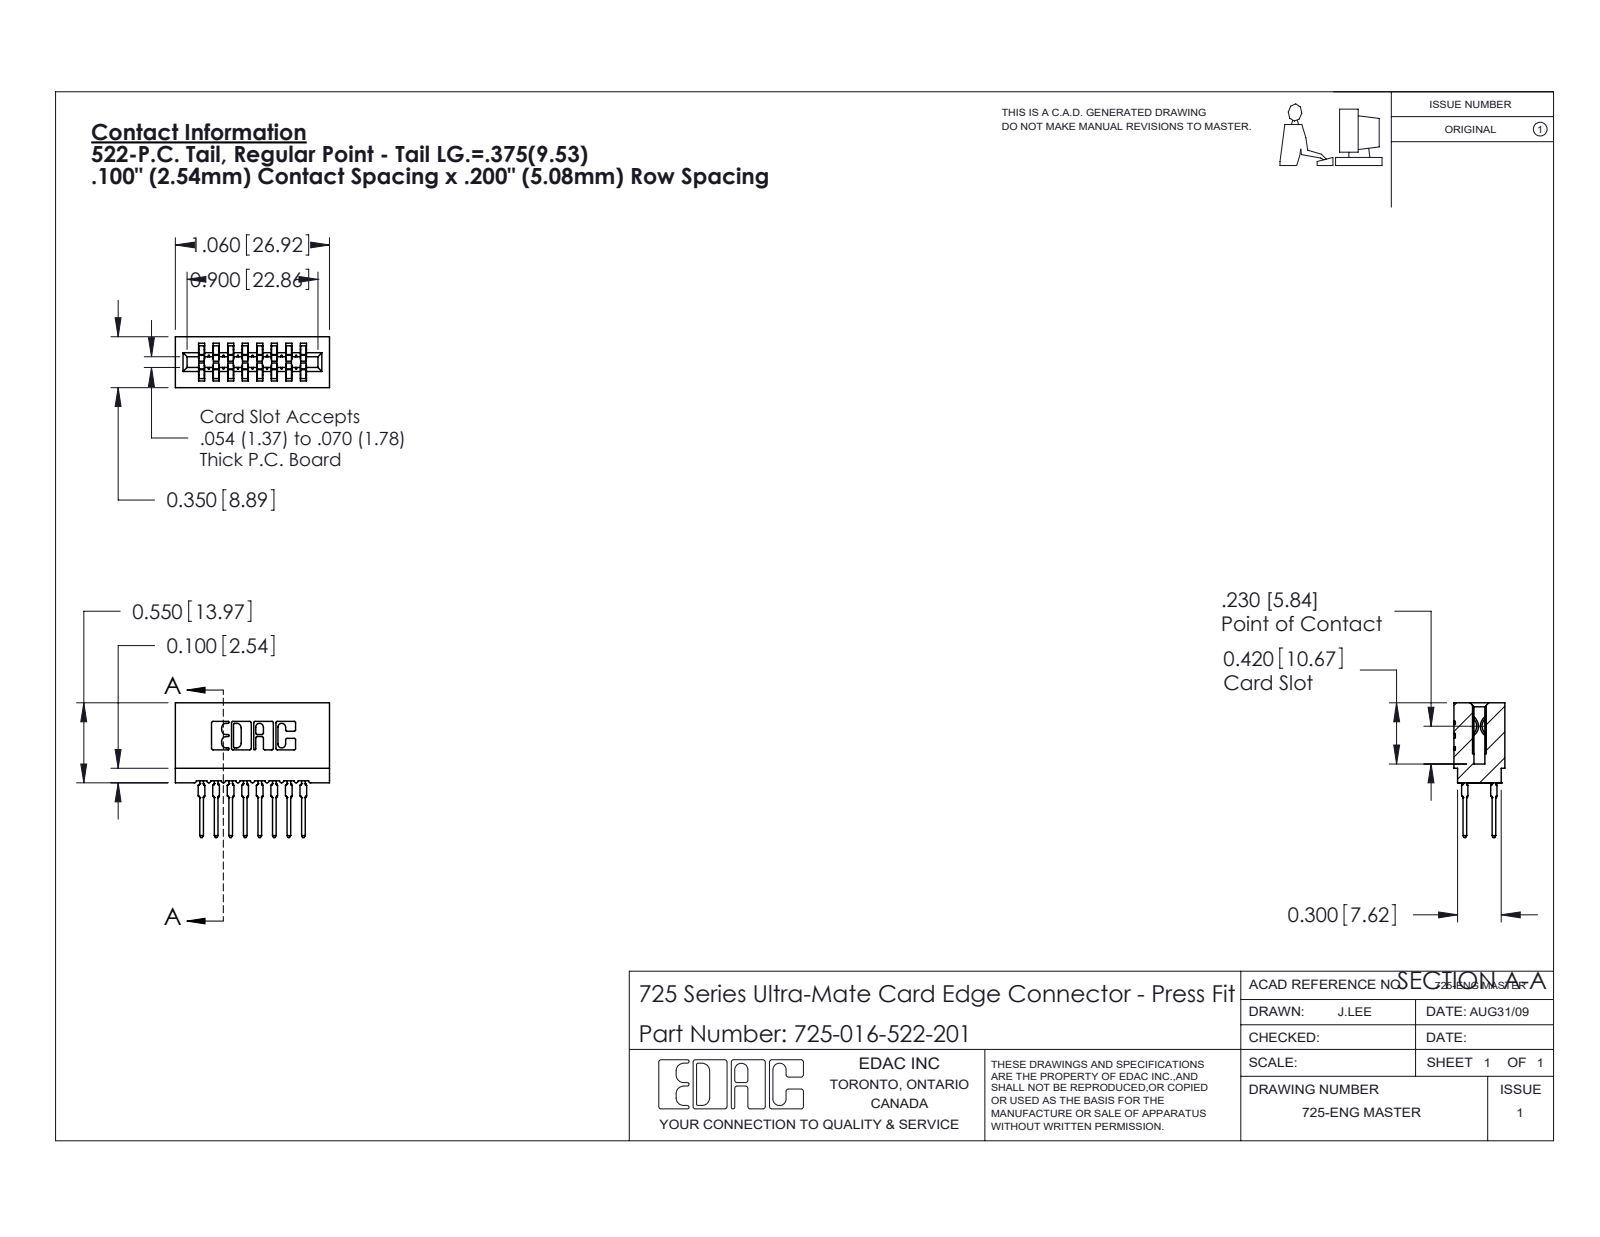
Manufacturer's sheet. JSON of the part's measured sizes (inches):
{"part_name": "725-016-522-201; 745-292-001_522; 725 Part_Insulator Option - 01", "step_written_by": "SolidWorks 2020 (CONFIG_CONTROL_DESIGN)", "units": "inches", "bodies": {"solids": 17, "faces": 1527, "planar": 791, "cylindrical": 320, "other": 416}, "overall_size": [1.06, 0.926, 0.35], "volume_in3": 0.142, "surface_area_in2": 6.57, "partial_cylinders_radius": [[0.021, 32], [0.01, 22], [0.015, 16], [0.005, 8], [0.011, 8], [0.007, 6], [0.031, 6], [0.026, 3]], "face_to_face_distances": [0.1, 0.2, 0.3, 0.4, 0.042, 0.142, 0.058, 0.5, 0.242, 0.158]}
